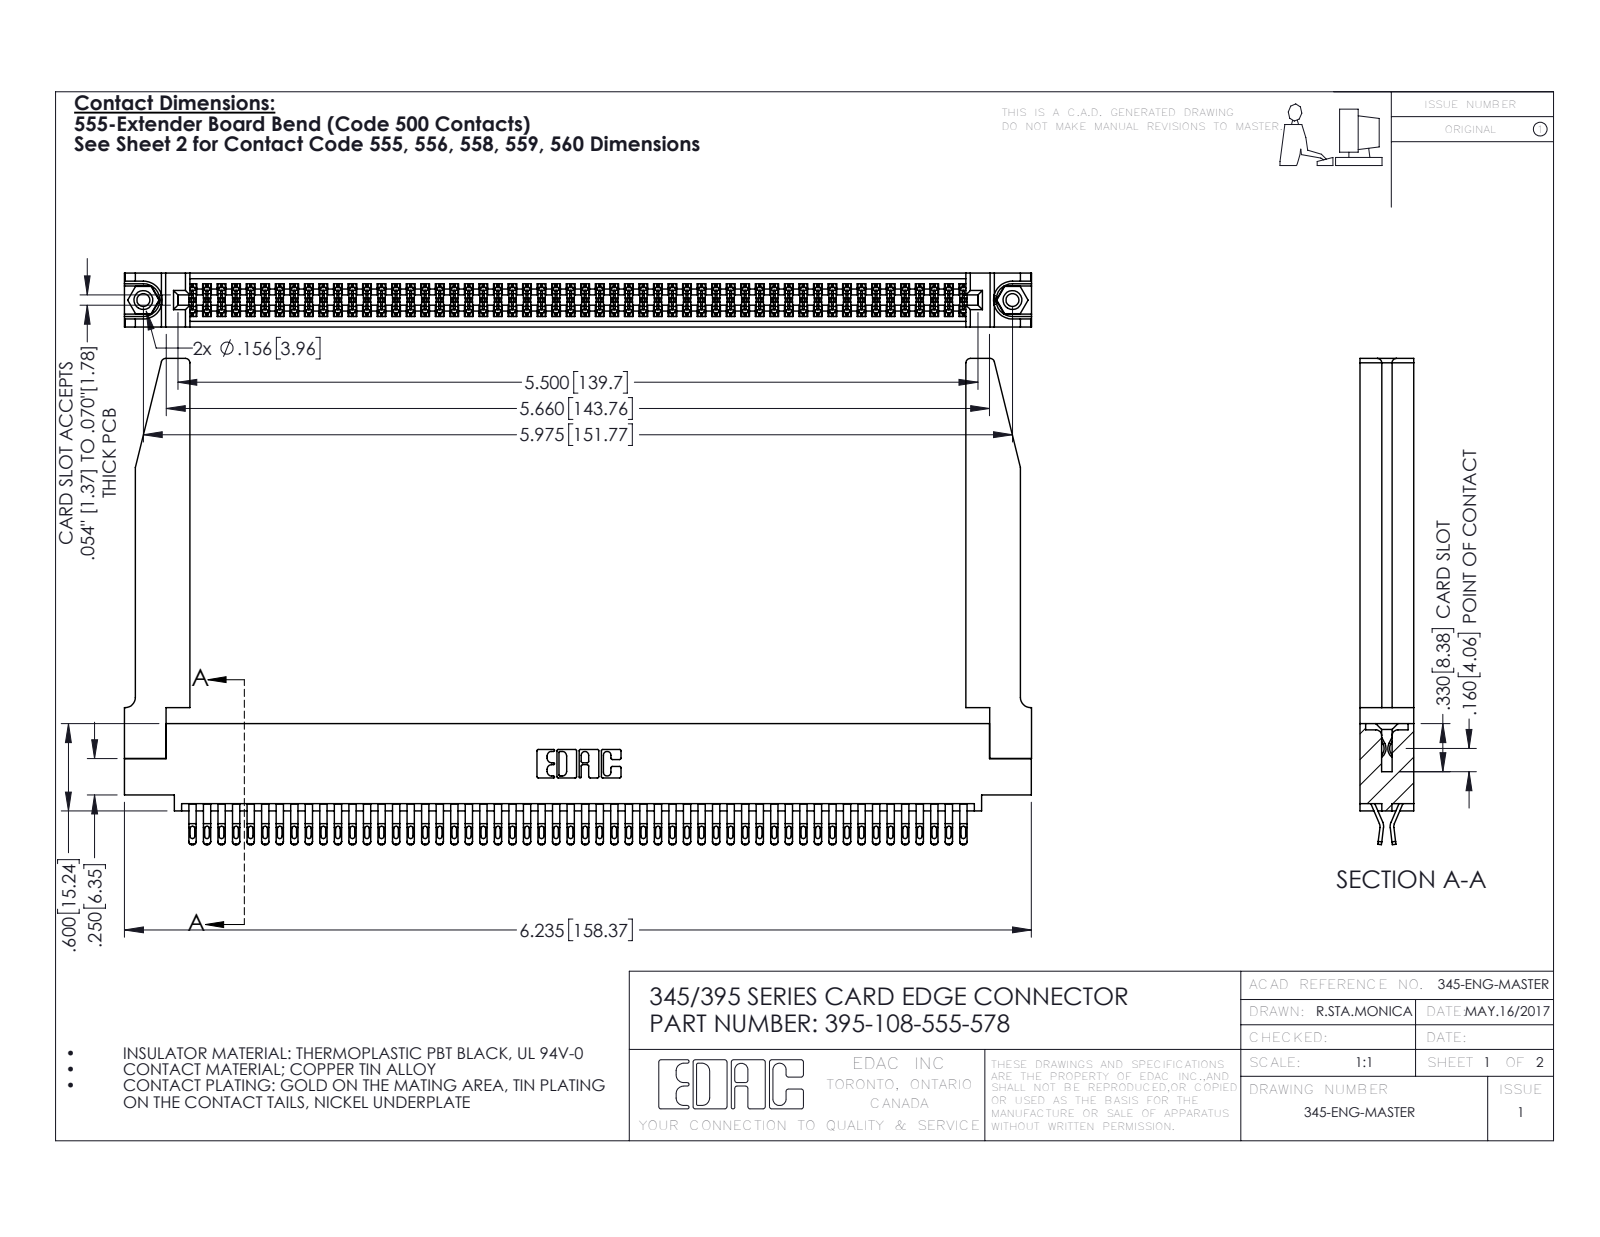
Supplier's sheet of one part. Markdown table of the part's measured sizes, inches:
| quantity | value |
| --- | --- |
| part name | 345-250-001_345-250-001-102; 345-220-078_345-220-078; 395-108-555-578; 345-292-001_555 Tail (+1 more) |
| STEP written by | SolidWorks 2016 (CONFIG_CONTROL_DESIGN) |
| units | inches |
| bodies | 113 solids, 6412 faces (3574 planar, 2786 cylindrical, 52 other) |
| overall size | 6.236 × 3.342 × 0.37 |
| volume | 1.435 in³ |
| surface area | 48.85 in² |
| round holes (diameter × count) | 0.089 × 2, 0.125 × 2, 0.156 × 2, 0.064 × 1 |
| round bosses / shafts (diameter × count) | 0.155 × 2 |
| partial cylindrical surfaces (radius × count) | 0.016 × 270, 0.02 × 216, 0.006 × 162, 0.01 × 22, 0.03 × 8, 0.007 × 6, 0.031 × 6, 0.026 × 3 |
| main face-to-face distances | 0.072, 0.37, 0.298, 0.025, 0.2, 0.098, 0.272, 0.225, 0.175, 0.148 |
| hole center spacings | 0.27, 5.739, 5.975 |
